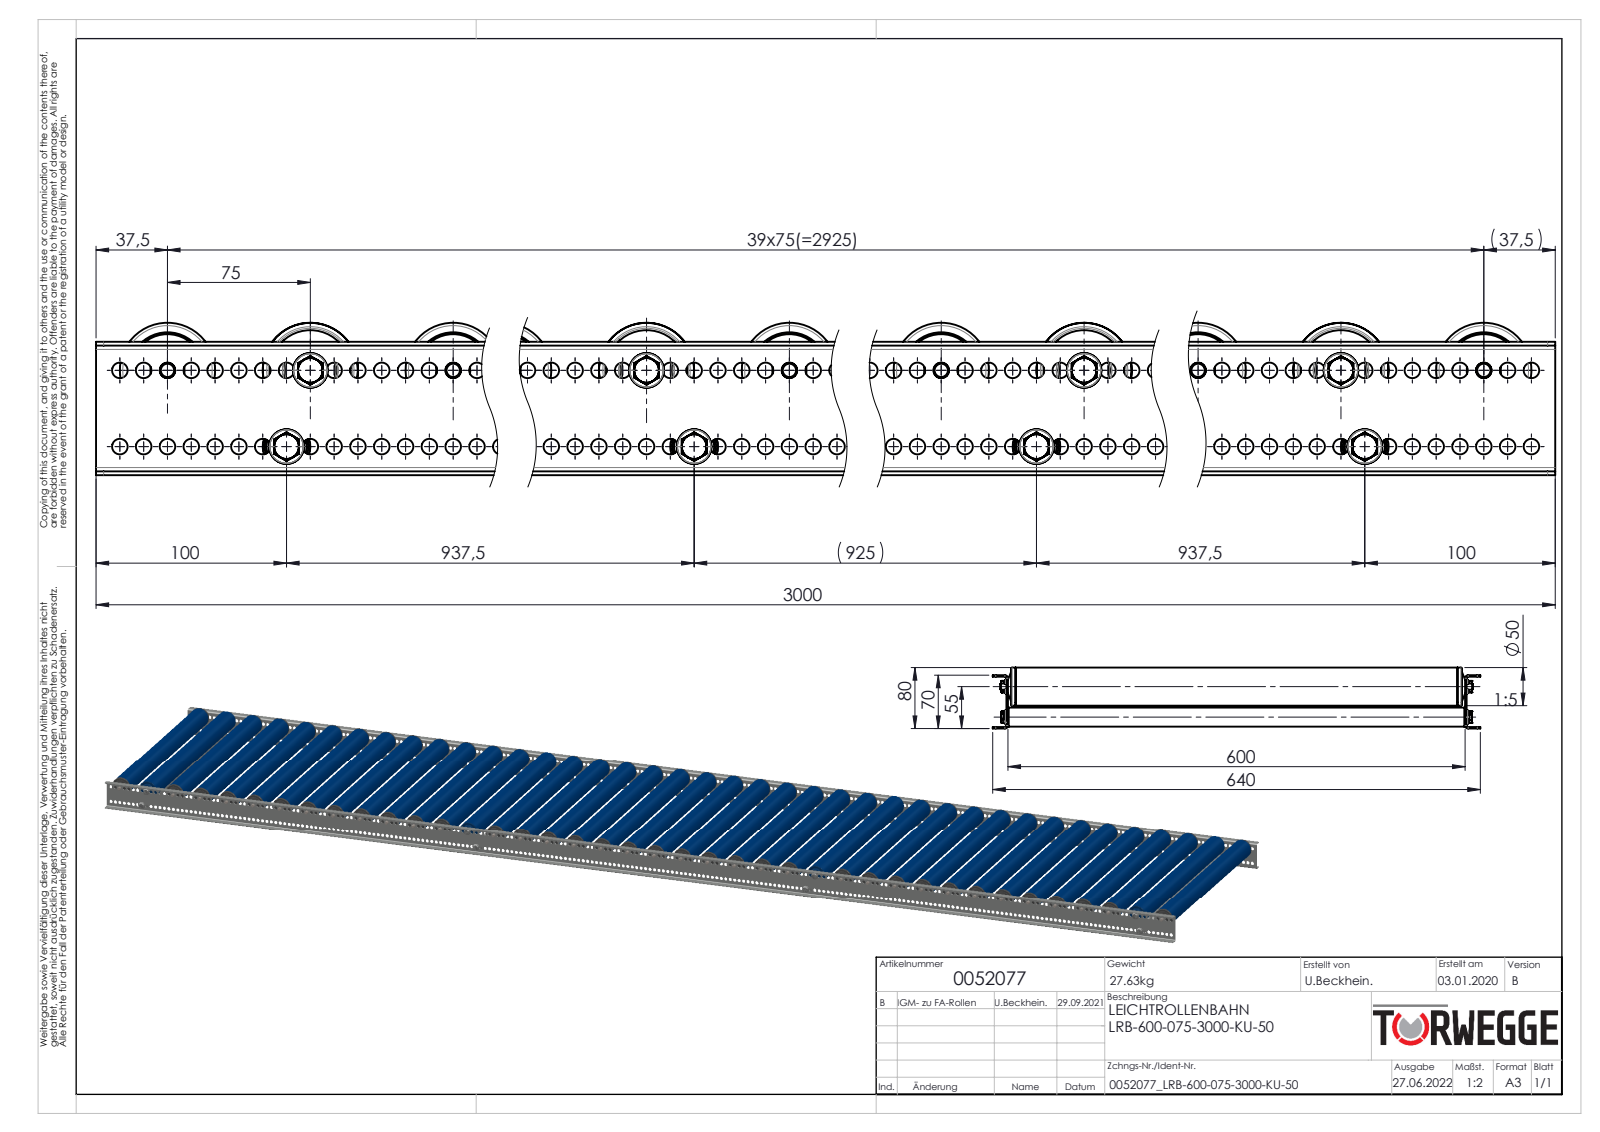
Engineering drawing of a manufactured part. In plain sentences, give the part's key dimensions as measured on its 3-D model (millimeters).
The part is named "0039780-Achse-ST-Ø12-KFG_IGM8-AL=600; 0024178_Passscheibe_DIN988_12x18x1; Traversen_KFG_L600; 0026266_Typ-KUT100-50x2,8-12 (+8 more)". Its 3-D file was written by "SolidWorks 2020 (AUTOMOTIVE_DESIGN)". It is 634 solids with 12220 faces: 3052 planar, 5720 cylindrical and 3448 other. Overall it measures 3000 by 640 by 80 millimeters. Its volume is 14 750 000 cubic millimeters and its surface area 10 820 000 square millimeters. Round holes: 478 of diameter 8.2, 36 of diameter 7.6, 36 of diameter 8, 36 of diameter 25, 36 of diameter 30, 36 of diameter 35, 36 of diameter 39.4, 36 of diameter 40, 8 of diameter 6.8, 4 of diameter 12, 4 of diameter 12.1, 4 of diameter 16. Round bosses or shafts: 40 of diameter 50, 36 of diameter 44.4, 36 of diameter 38, 36 of diameter 36, 36 of diameter 33, 36 of diameter 22, 36 of diameter 21, 8 of diameter 25. Partial cylindrical surfaces (rounded edges, fillets, slot ends): 72 of radius 0.6, 72 of radius 0.75, 72 of radius 2.45, 36 of radius 4.87, 36 of radius 7, 8 of radius 4, 4 of radius 2, 4 of radius 2.5. The main face-to-face distances are 2, 602, 68, 600, 604, 70, 66, 592, 12, 6. The hole center spacings are 12.5, 25, 37.5, 50, 62.5, 75, 87.5, 100.
